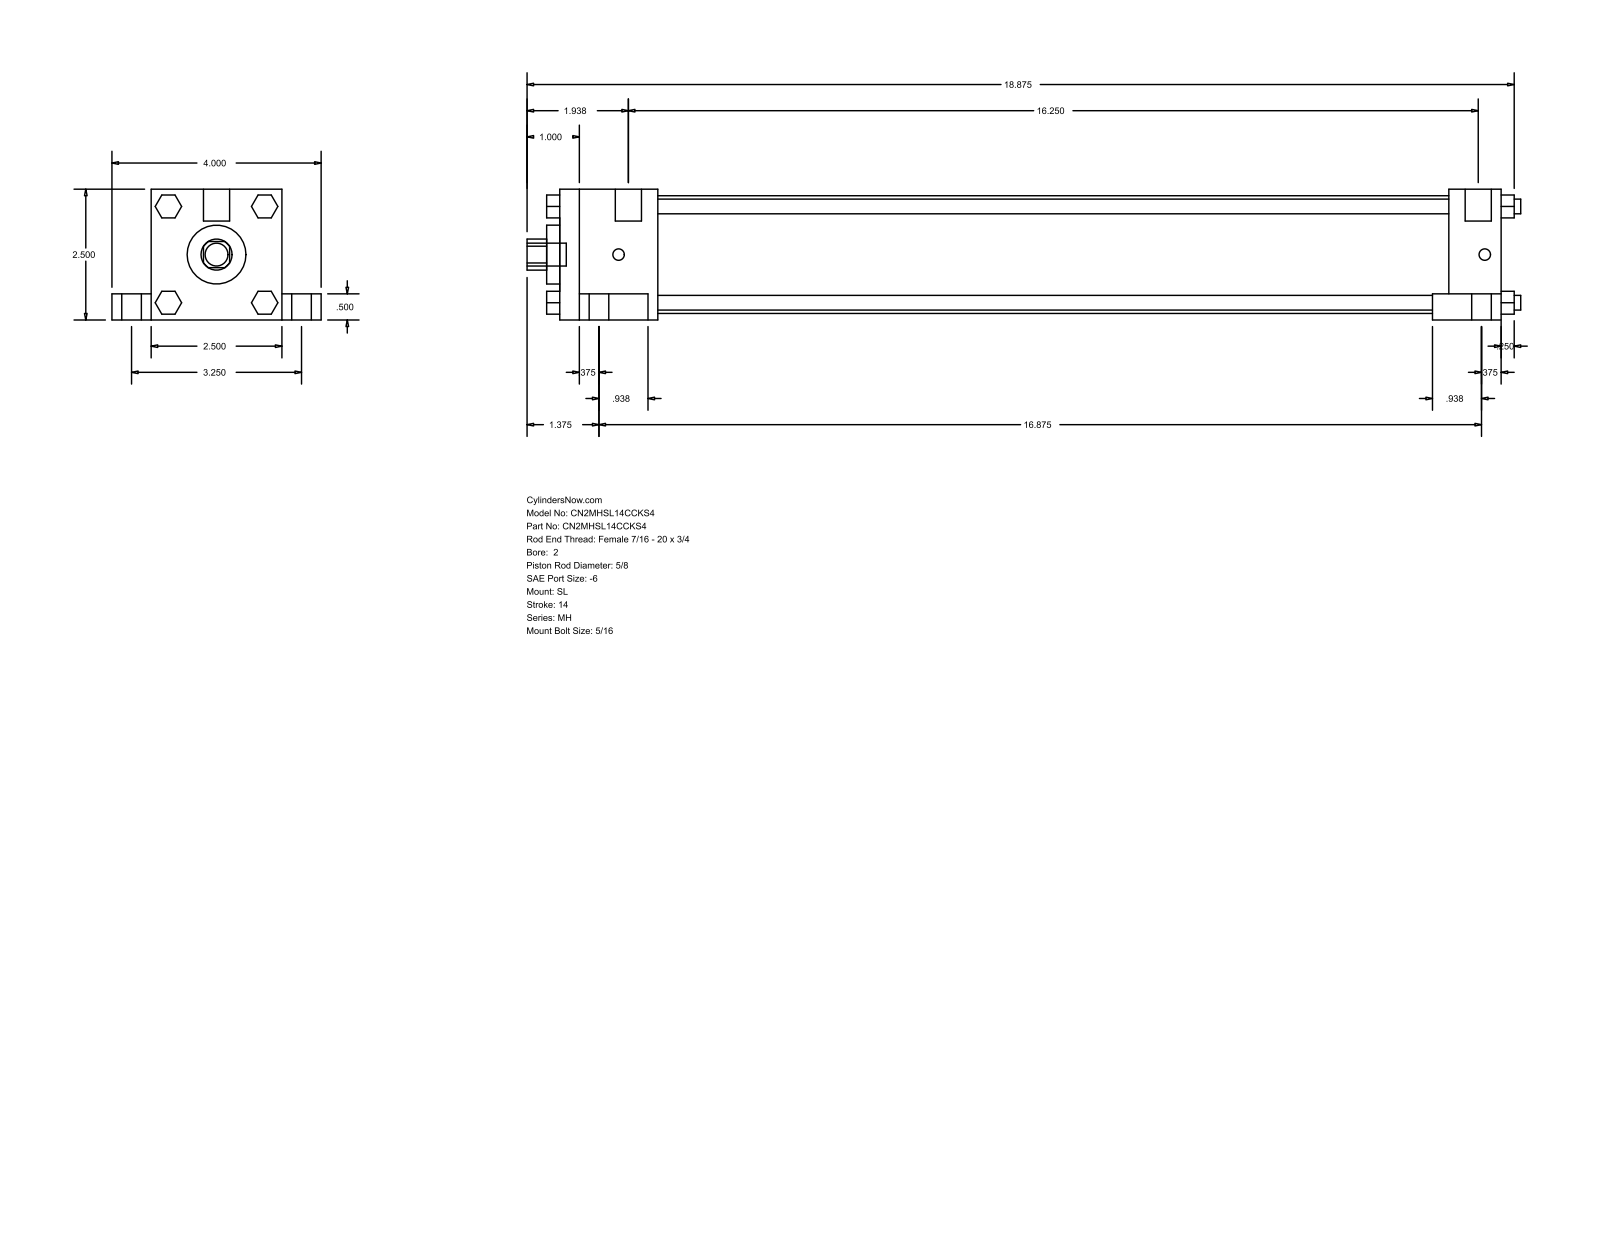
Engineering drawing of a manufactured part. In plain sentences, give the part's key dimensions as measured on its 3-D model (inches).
The part is named "MH_SL__0200_0.625". Its 3-D file was written by "GSSL Pune (CONFIG_CONTROL_DESIGN)". It is 0 solids with 148 faces: 112 planar, 36 cylindrical and 0 other. Overall it measures 19 by 4 by 2.5 inches. Round holes: 1 of diameter 0.625, 1 of diameter 1.125, 1 of diameter 2.25. Round bosses or shafts: 4 of diameter 0.625, 4 of diameter 0.375, 4 of diameter 0.281, 4 of diameter 0.219, 2 of diameter 0.5, 1 of diameter 0.437. Partial cylindrical surfaces (rounded edges, fillets, slot ends): 1 of radius 0.297. The main face-to-face distances are 2.5, 18, 0.5, 0.75, 2, 3.25, 17, 1, 1.875, 15.125.
